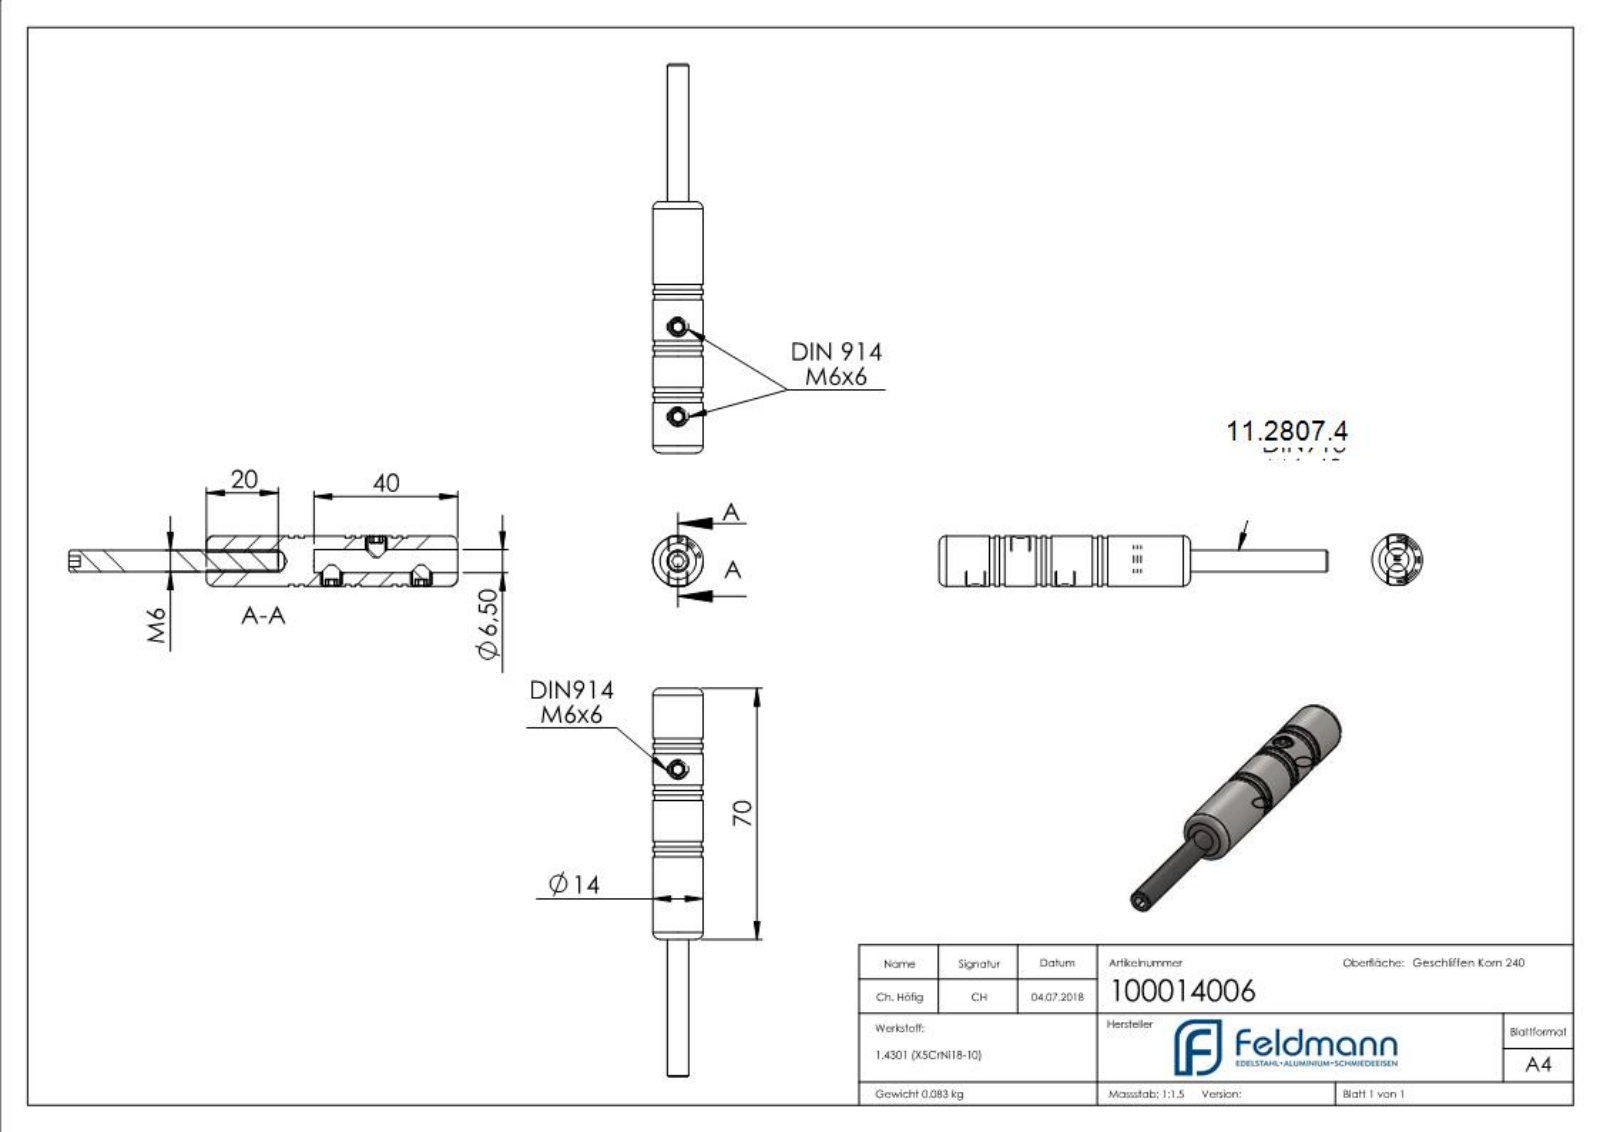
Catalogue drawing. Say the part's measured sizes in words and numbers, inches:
The part is named "10001X00X Teil 1_100014006 Teil1; DIN914_DIN 914 M6x6; 100014006; DIN913_DIN913 M6x60". Its 3-D file was written by "SolidWorks 2015 (CONFIG_CONTROL_DESIGN)". It is 5 solids with 430 faces: 160 planar, 98 cylindrical and 172 other. Overall it measures 4.262 by 0.551 by 0.551 inches. Its volume is 0.643 cubic inches and its surface area 9.911 square inches. Round holes: 4 of diameter 0.197, 1 of diameter 0.256. Round bosses or shafts: 4 of diameter 0.236, 1 of diameter 0.551, 1 of diameter 0.512. Partial cylindrical surfaces (rounded edges, fillets, slot ends): 50 of radius 0.008. The main face-to-face distances are 0.059, 0.11, 0.512, 0.618, 1.13, 0.051, 0.402, 0.453, 0.169, 1.181. The hole center spacings are 0.492, 0.984.
